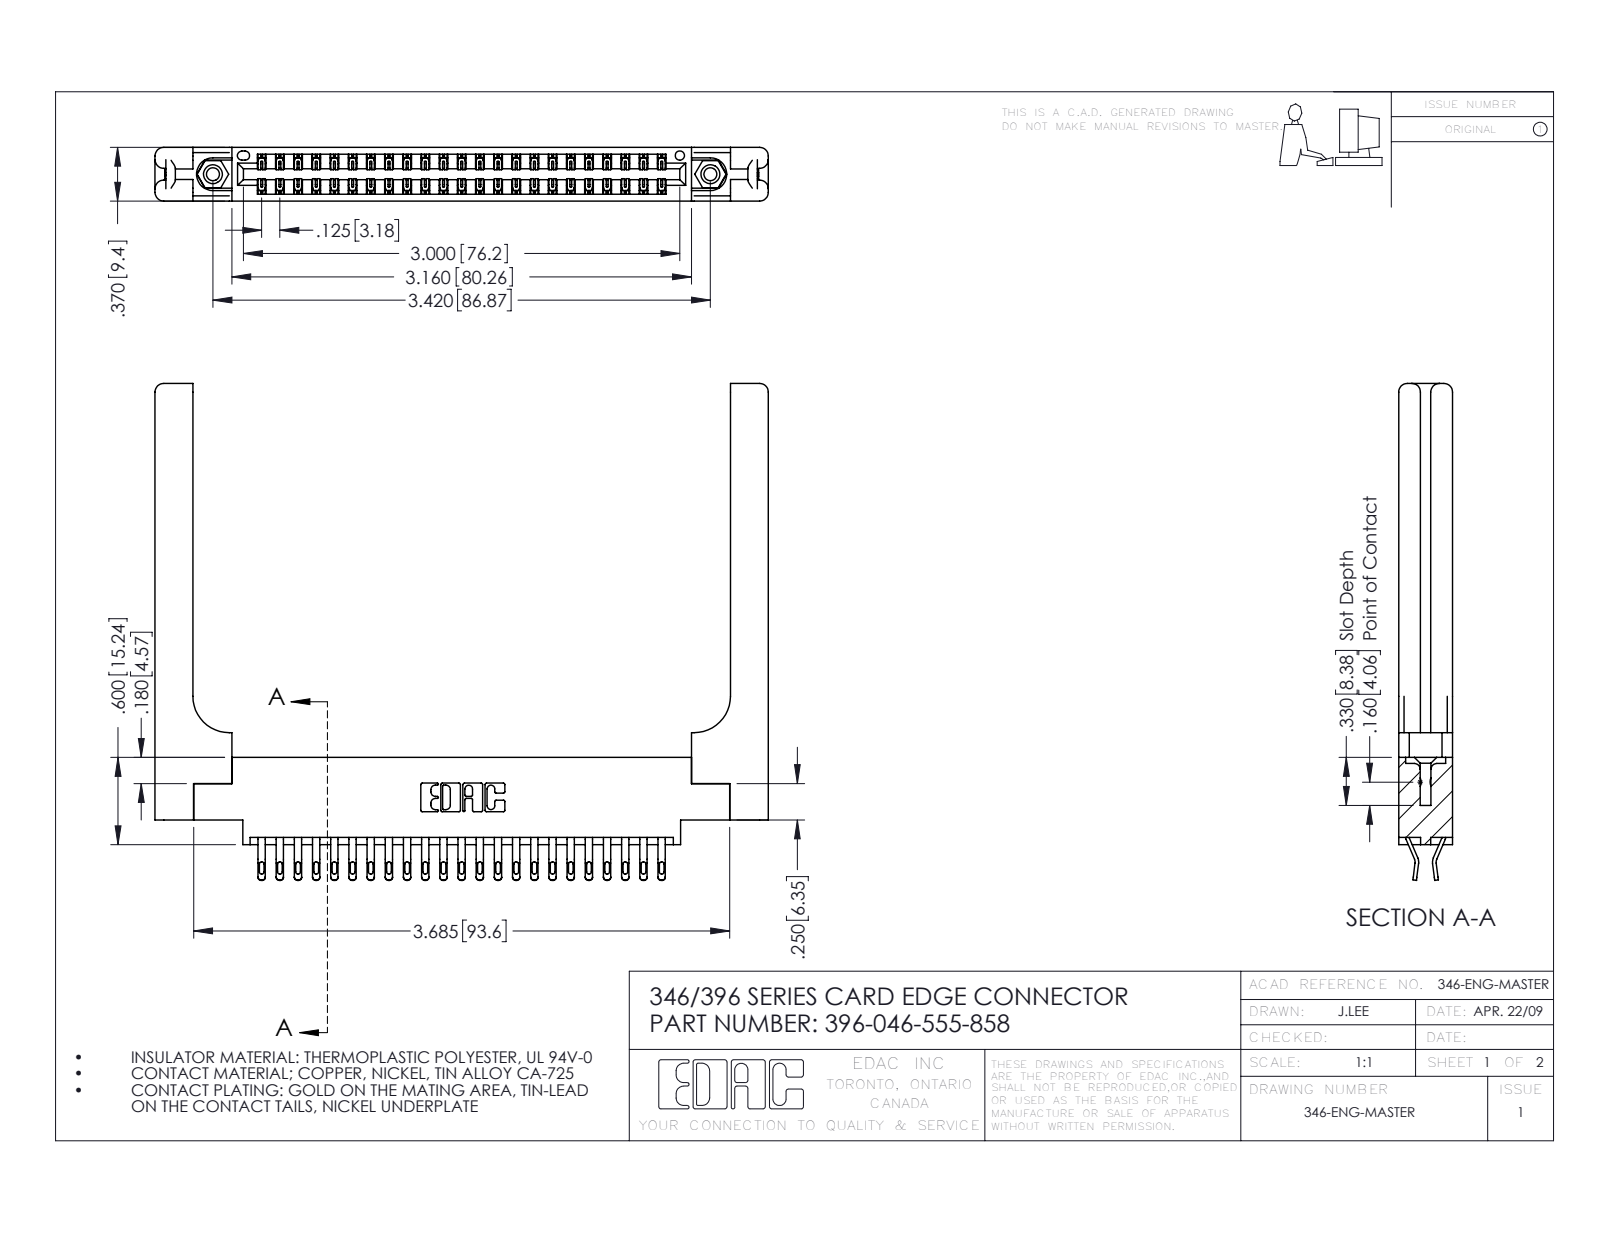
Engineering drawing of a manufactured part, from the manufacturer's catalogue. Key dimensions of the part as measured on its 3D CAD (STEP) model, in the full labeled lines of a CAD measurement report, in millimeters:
Part name (STEP PRODUCT): 346-220-058_345-220-058; 345-250-001_345-250-001-102; 345-292-001_555 Tail; 396-046-555-858 (+1 more)
STEP written by: SolidWorks 2016 (CONFIG_CONTROL_DESIGN)
Units: millimetres
Bodies: 51 solids, 3050 faces (1746 planar, 1244 cylindrical, 60 other)
Overall size (bounding box): 107.1 × 86.7 × 9.4
Volume: 17 760 mm³ · Surface area: 19 450 mm²
Round holes (diameter × count): ⌀2.3 ×2, ⌀3.2 ×2, ⌀4 ×2, ⌀1.6 ×1
Round bosses / shafts (diameter × count): ⌀3.9 ×2
Partial cylindrical surfaces — rounded edges, fillets, slot ends (radius × count): R0.4 ×92, R0.5 ×92, R0.2 ×69, R0.3 ×22, R1.5 ×16, R0.2 ×6, R0.8 ×6, R0.7 ×3
Main face-to-face distances: 9.4, 1.8, 1.2, 8.2, 3.8, 3.8, 6.4, 0.6, 7.6, 2
Hole centre spacings: 6.2, 81.6, 86.9
